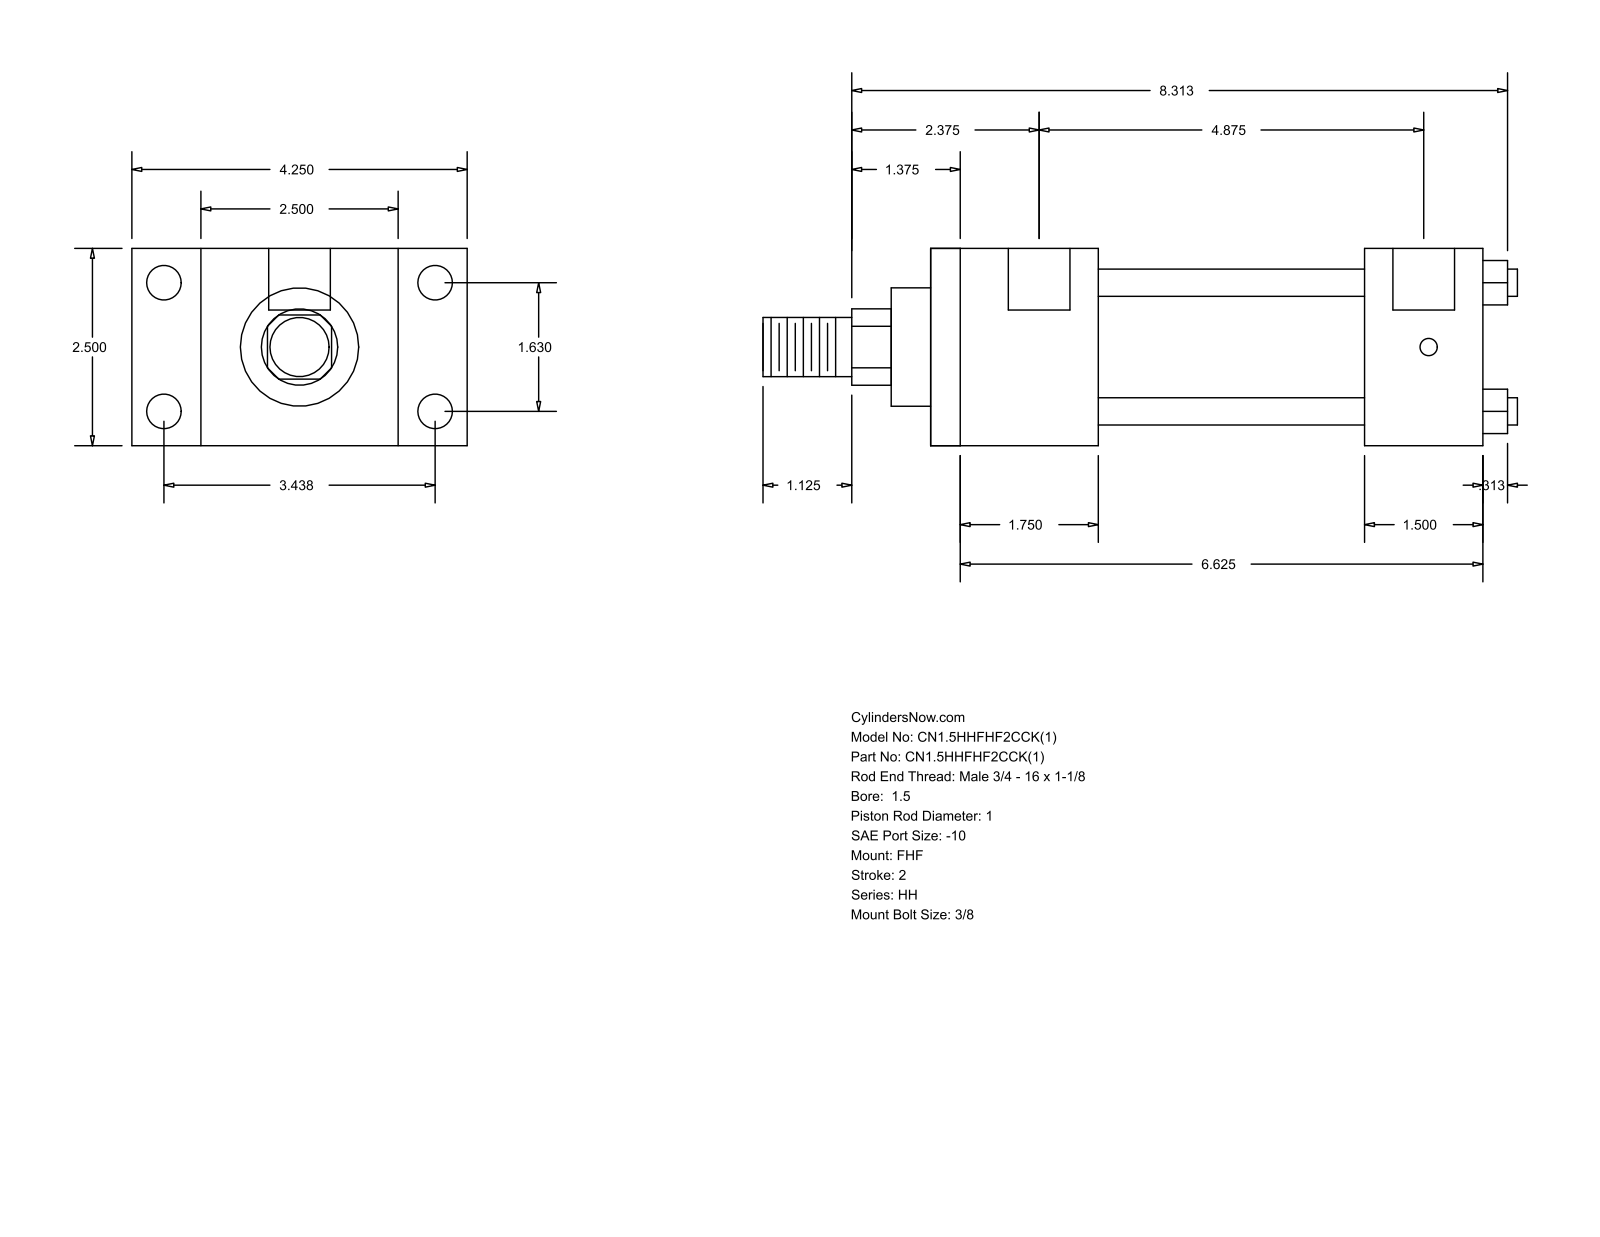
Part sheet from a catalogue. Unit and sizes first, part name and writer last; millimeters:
Units: millimetres
Overall size (bounding box): 242.89 × 107.95 × 63.5
Round holes (diameter × count): ⌀5.56 ×4, ⌀11.13 ×4, ⌀19.84 ×2
Round bosses / shafts (diameter × count): ⌀8.76 ×4, ⌀44.45 ×1, ⌀38.1 ×1, ⌀25.4 ×1, ⌀19.05 ×1
Partial cylindrical surfaces — rounded edges, fillets, slot ends (radius × count): R12.29 ×1
Main face-to-face distances: 63.5, 22.23, 85.73, 53.98, 107.96, 177.8, 123.82, 38.1, 85.72, 139.7
Hole centre spacings: 1.59, 41.4, 87.32, 96.64, 125.41, 127, 123.82
Bodies: 0 solids, 88 faces (60 planar, 28 cylindrical, 0 other)
Part name (STEP PRODUCT): HH_FHF__0150_1
STEP written by: GSSL Pune (CONFIG_CONTROL_DESIGN)
